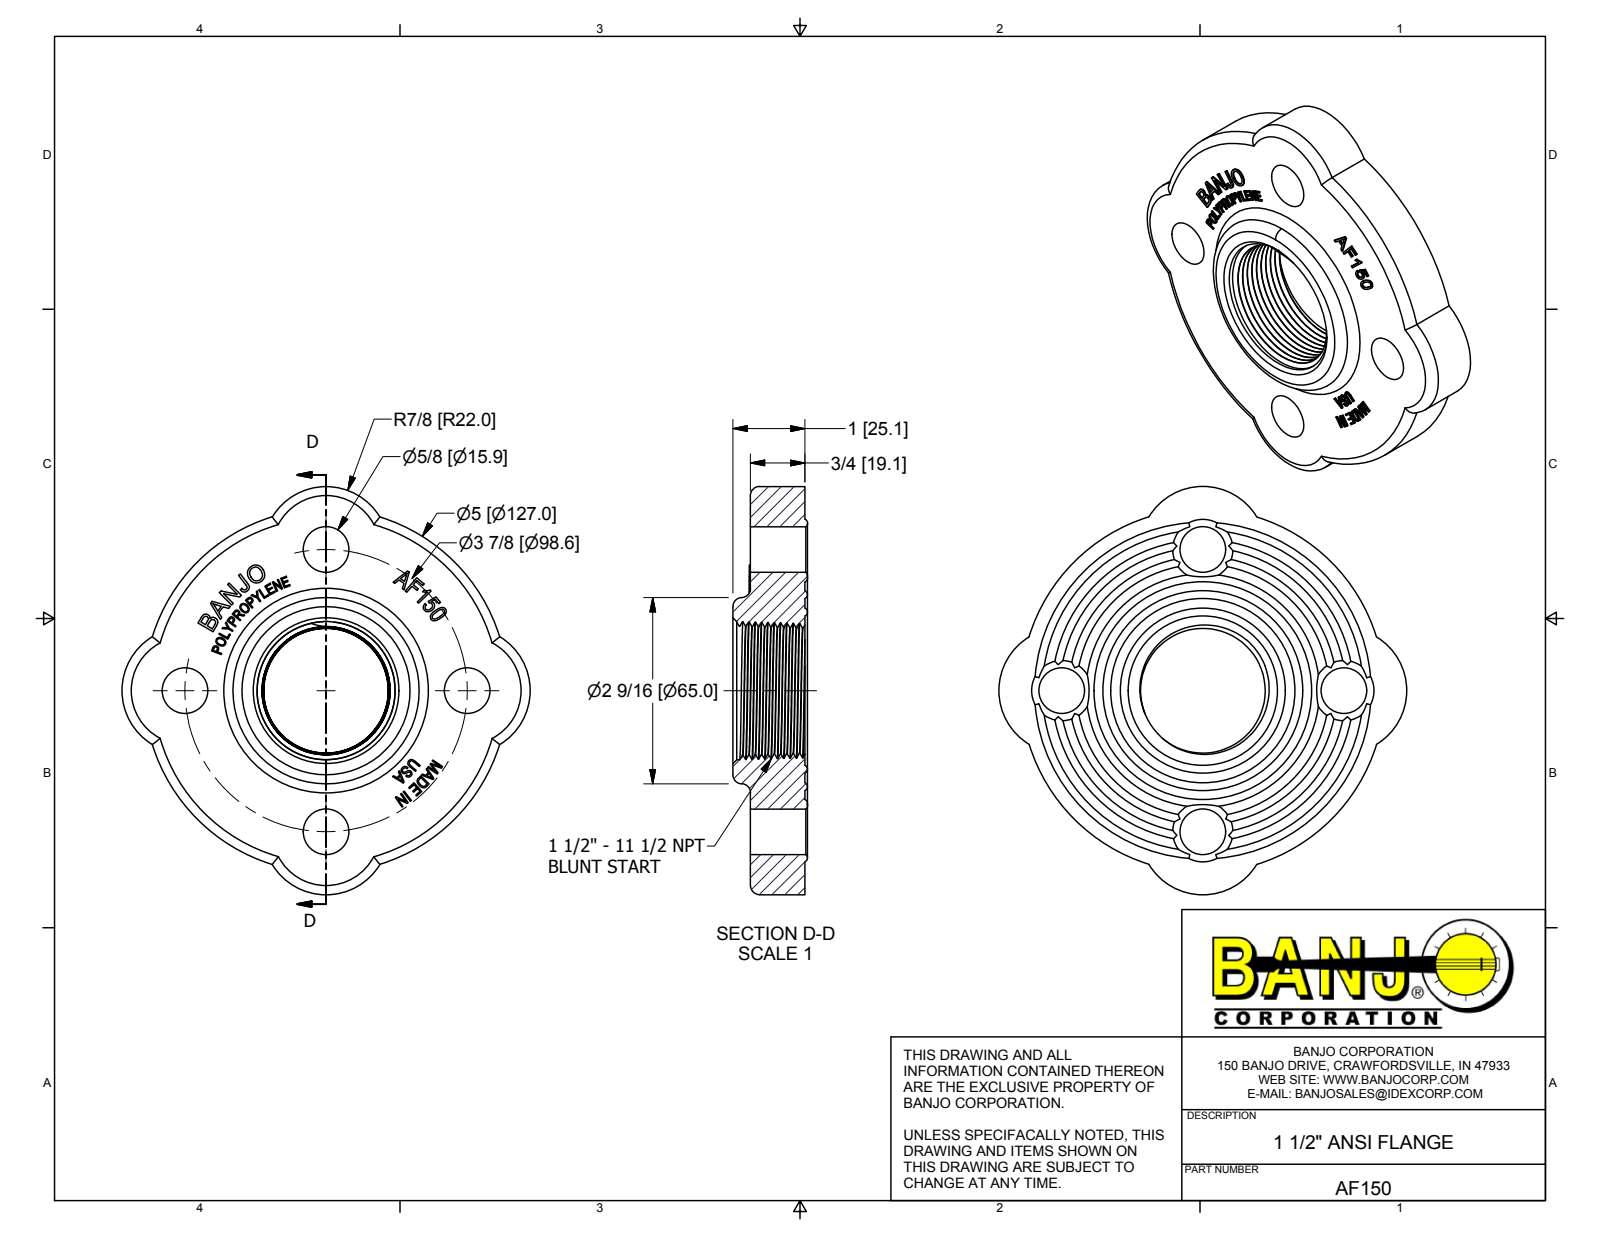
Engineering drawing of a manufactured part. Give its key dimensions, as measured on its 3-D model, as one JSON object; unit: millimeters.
{"part_name": "AF150", "step_written_by": "Autodesk Inventor 2016 (AUTOMOTIVE_DESIGN)", "units": "millimeters", "bodies": {"solids": 1, "faces": 479, "planar": 307, "cylindrical": 13, "other": 159}, "overall_size": [142.49, 142.49, 26.04], "volume_mm3": 221881, "surface_area_mm2": 41795, "round_holes": [[15.88, 4]], "partial_cylinders_radius": [[21.97, 4], [13.74, 1], [63.5, 1]], "face_to_face_distances": [19.05, 6.1, 25.15, 0.38, 19.43, 5.72, 0.42, 0.44, 0.72, 0.77], "hole_center_spacings": [69.69, 98.56]}
